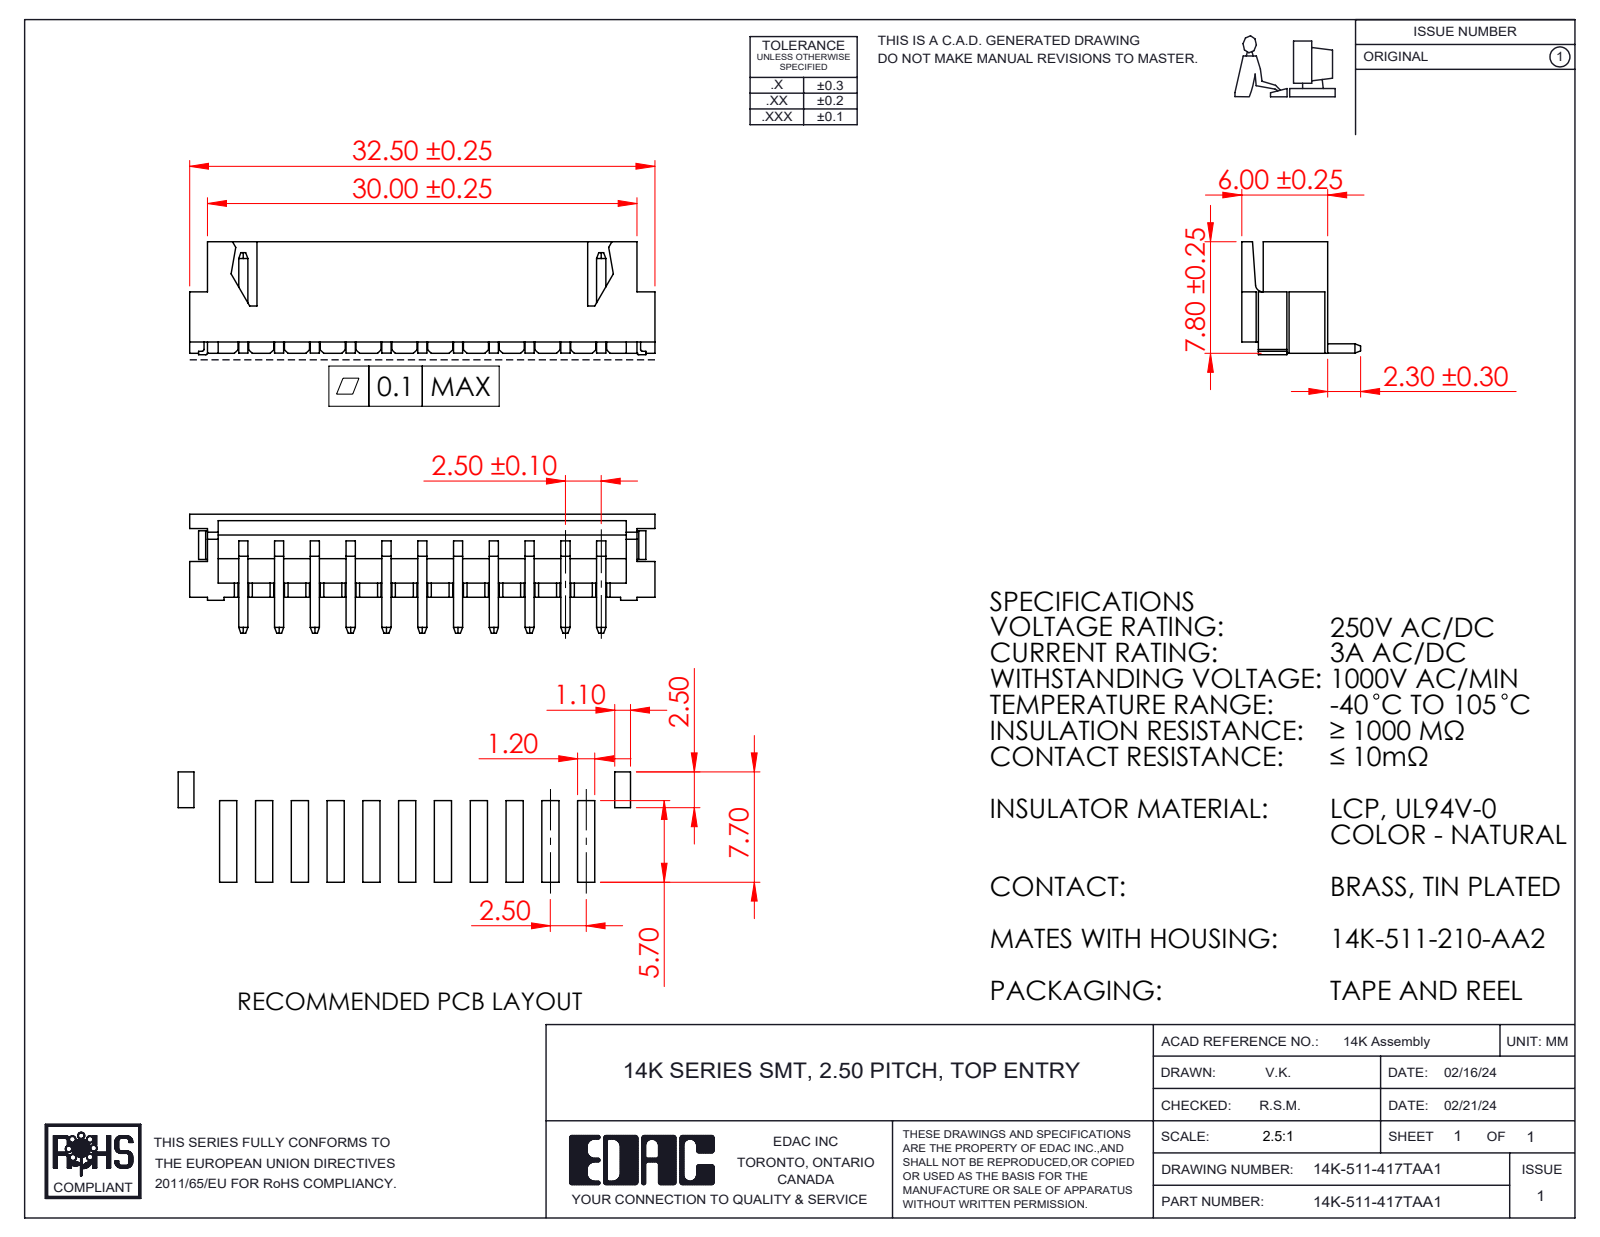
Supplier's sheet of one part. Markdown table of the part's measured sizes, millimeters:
| quantity | value |
| --- | --- |
| part name | 14K-511-418TAA1; 14K Series SMT Pin_Top Entry; 14K Series SMT Top Entry Insulator_511 |
| STEP written by | SolidWorks 2023 (CONFIG_CONTROL_DESIGN) |
| units | millimeters |
| bodies | 12 solids, 566 faces (516 planar, 50 cylindrical, 0 other) |
| overall size | 32.5 × 8.3 × 7.9 |
| volume | 582 mm³ |
| surface area | 1 849 mm² |
| partial cylindrical surfaces (radius × count) | 0.38 × 22, 0.12 × 4, 0.43 × 1, 0.5 × 1, 1.07 × 1 |
| main face-to-face distances | 0.75, 5.05, 5.8, 2.5, 0.64, 4.3, 1, 5, 1.86, 1.25 |
